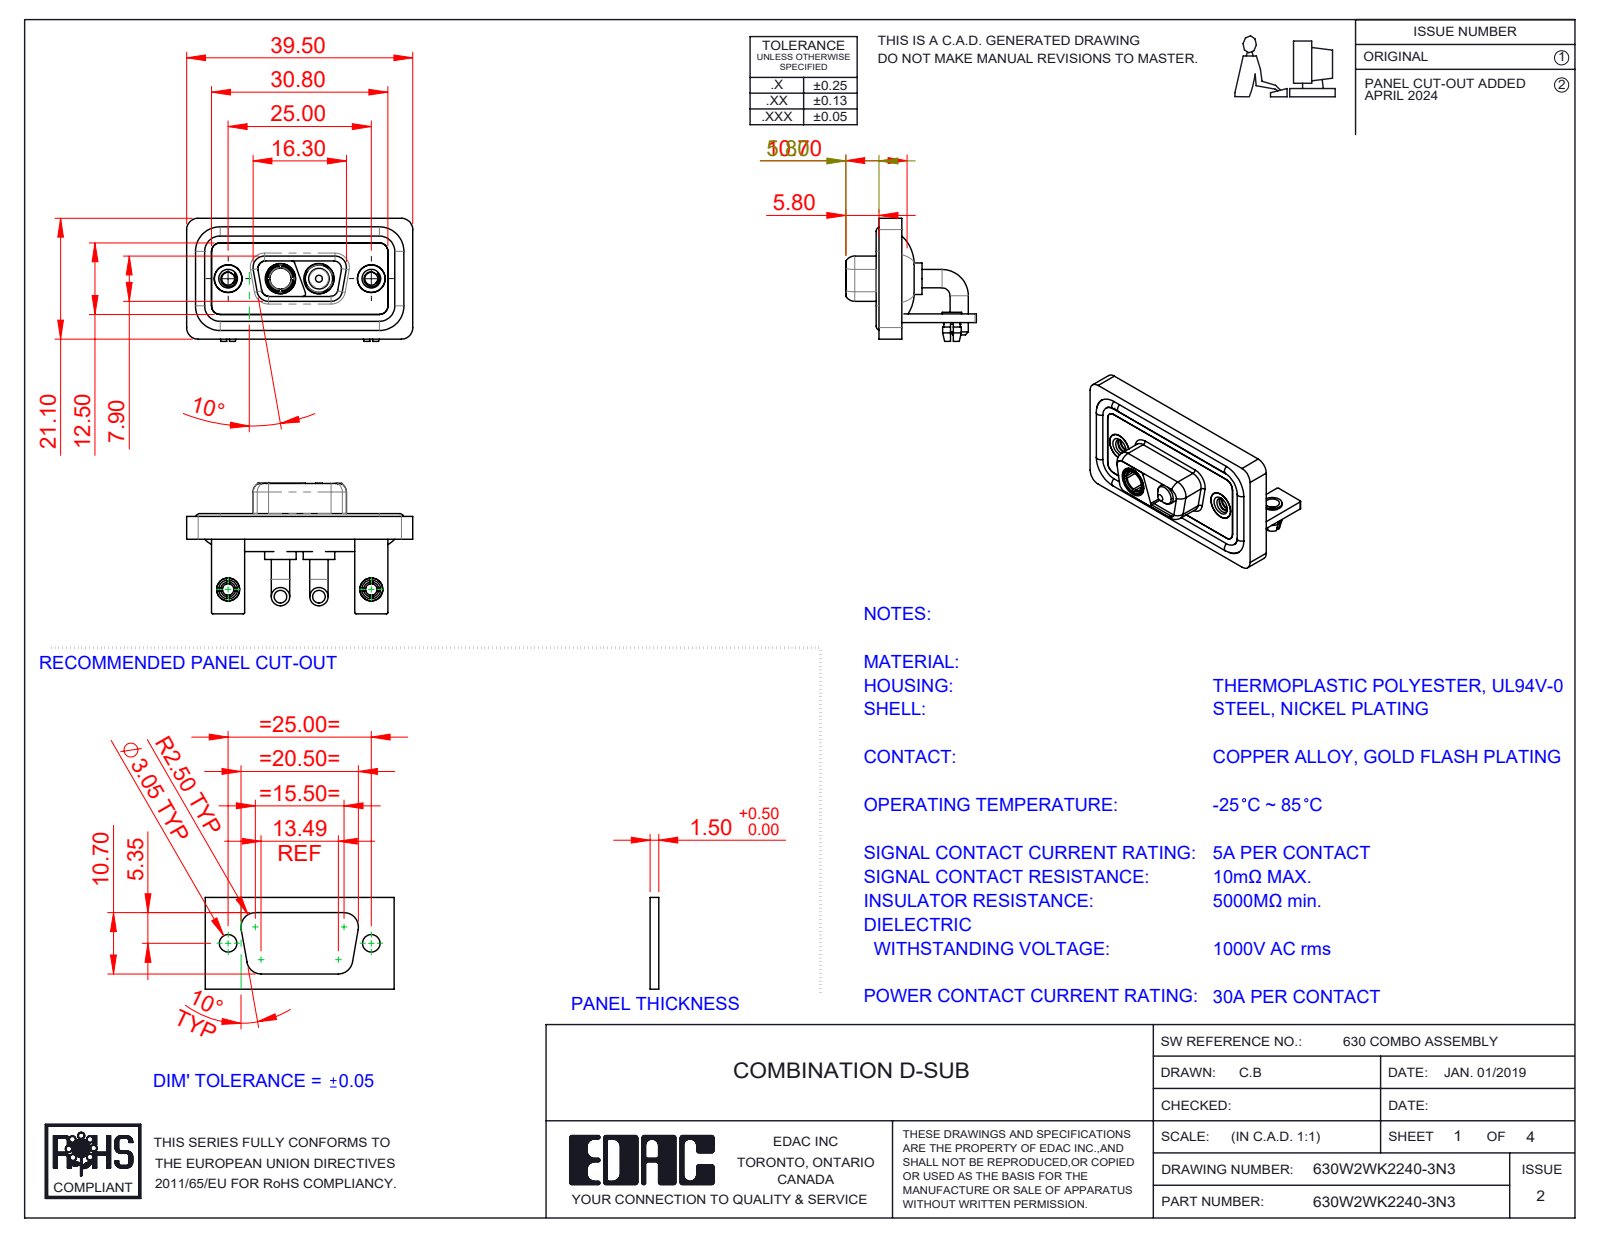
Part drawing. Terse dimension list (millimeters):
name: Power Pin_30A RA; 630Combo Shell Front_09 Contacts; Power Socket_30A RA; 630Combo Stabilizer Bracket_50 Contacts (+6 more)
written by: SolidWorks 2023 (CONFIG_CONTROL_DESIGN)
unit: mm
bodies: 15 solids, 648 faces (212 planar, 291 cylindrical, 145 other)
size: 39.5 × 22.8 × 21.5
volume: 5 165 mm³; area: 8 477 mm²
holes: 4× ⌀4.85, 2× ⌀2, 2× ⌀2.26, 2× ⌀2.5, 2× ⌀3.2, 2× ⌀4, 2× ⌀4.05, 2× ⌀5, 2× ⌀5.3, 1× ⌀3.7
bosses: 4× ⌀3.2, 4× ⌀1.6, 2× ⌀5.5, 2× ⌀5.2, 2× ⌀4.95, 2× ⌀4.8, 2× ⌀4.75, 2× ⌀4
rounds: 19× R2, 18× R1.5, 16× R0.25, 8× R1.35, 8× R1.6, 7× R0.5, 4× R0.6, 4× R0.65
face distances: 0.4, 2.9, 1.5, 1.1, 3.7, 1.8, 0.8, 2.5, 1.6, 3.1
hole spacings: 9.14, 15.86, 25, 6.72
